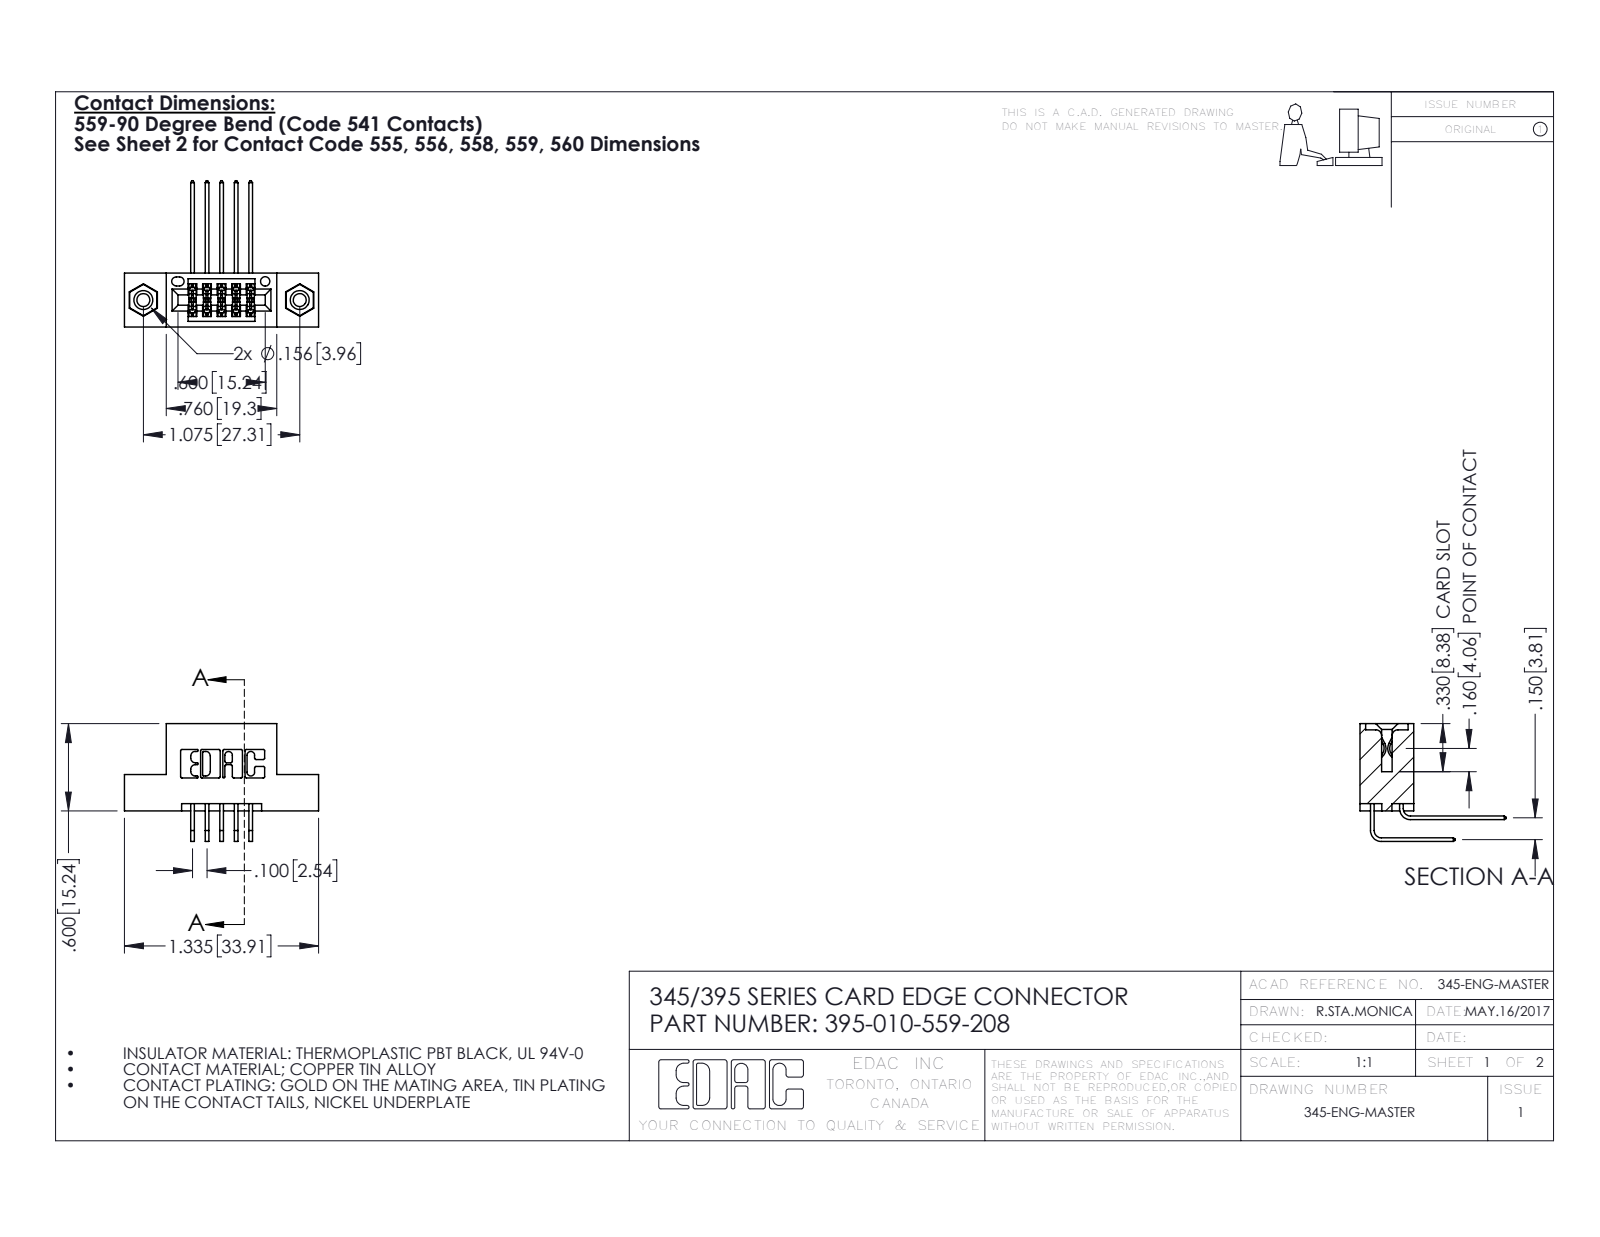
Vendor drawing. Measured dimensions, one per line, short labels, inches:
name: 345 Part_Flush Mounting Lugs - 0.156 Dia-TI; 395-010-559-208; 345-292-001_559 Tail - 2; 345-292-001_558 559 Tail - 1 (+1 more)
written by: SolidWorks 2016 (CONFIG_CONTROL_DESIGN)
unit: in
bodies: 13 solids, 706 faces (462 planar, 228 cylindrical, 16 other)
size: 1.335 × 1.005 × 0.809
volume: 0.183 in³; area: 6.208 in²
holes: 2× ⌀0.089, 2× ⌀0.125, 2× ⌀0.156, 1× ⌀0.064
bosses: 2× ⌀0.155
rounds: 22× R0.01, 16× R0.006, 6× R0.007, 6× R0.031, 3× R0.026, 2× R0.014, 2× R0.019, 2× R0.022
face distances: 0.2, 0.1, 0.37, 0.072, 0.298, 0.15, 0.098, 0.272, 0.025, 0.3
hole spacings: 0.27, 0.847, 1.075
